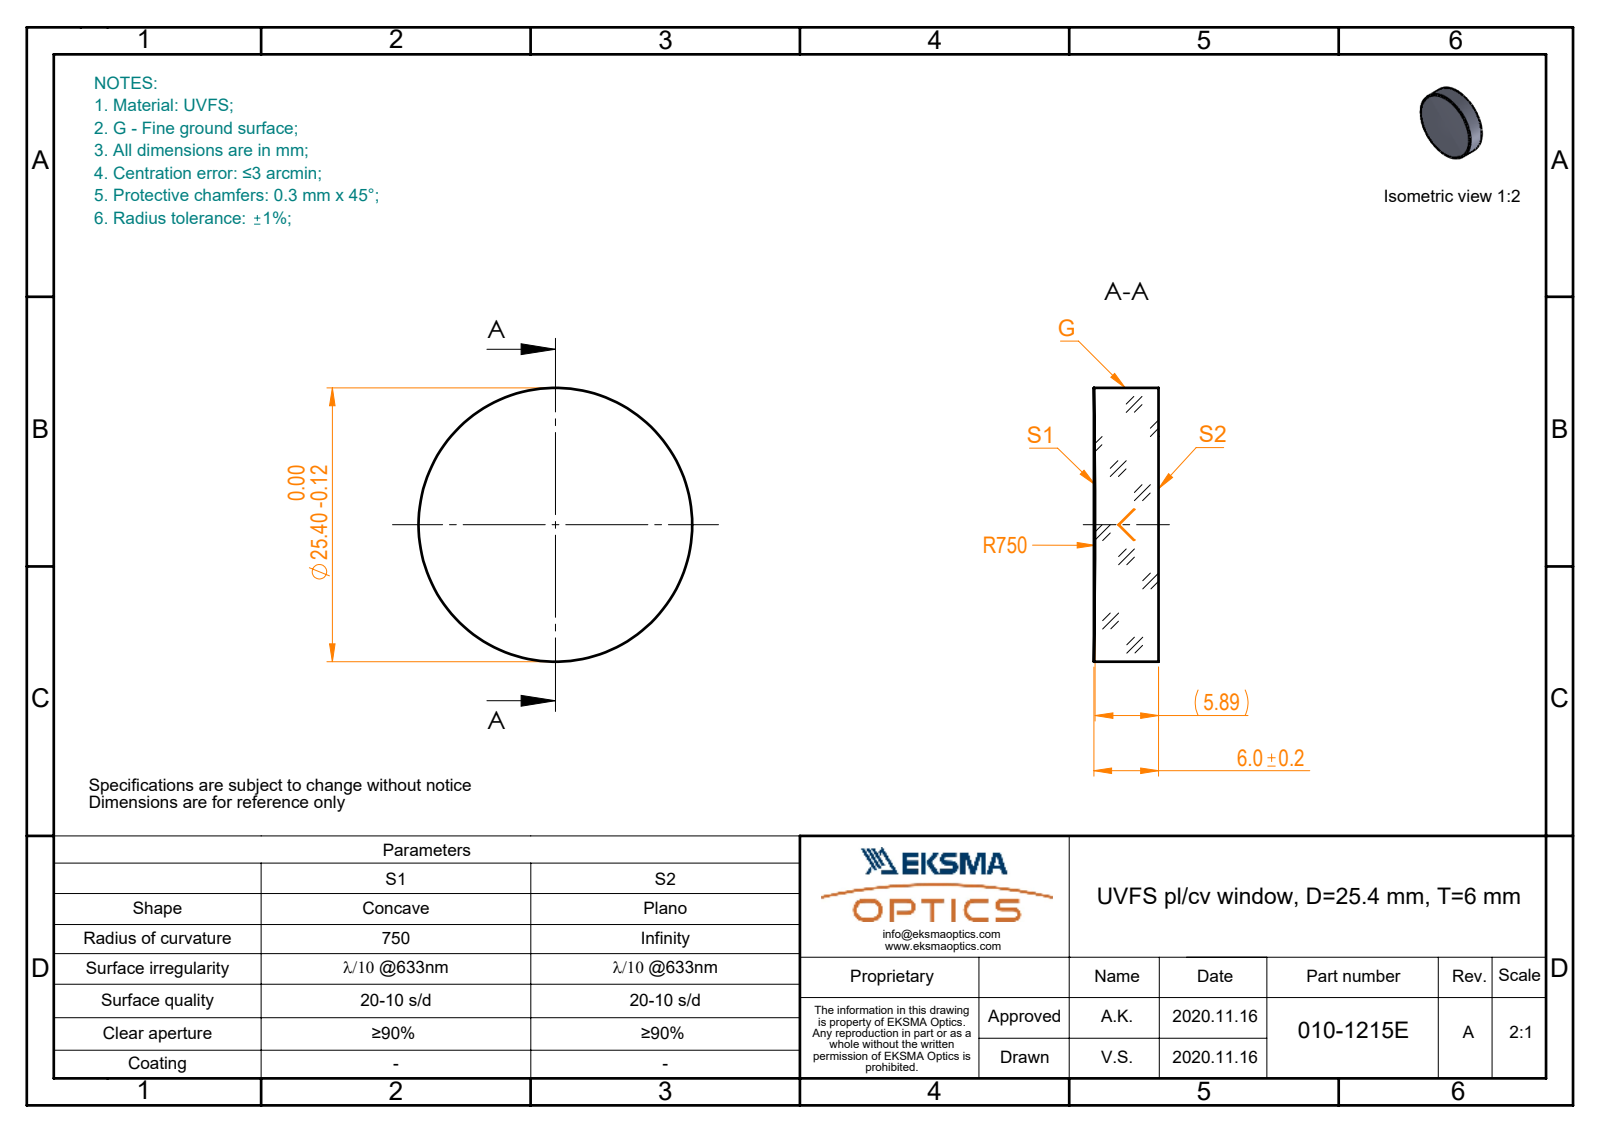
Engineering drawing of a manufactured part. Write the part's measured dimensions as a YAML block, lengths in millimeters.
part_name: "010-1215E_UVFS_PCV_window"
step_written_by: "SolidWorks 2019 (CONFIG_CONTROL_DESIGN)"
units: millimeters
bodies: {solids: 1, faces: 5, planar: 1, cylindrical: 2, other: 2}
overall_size: [25.4, 25.4, 6]
volume: 3013
surface_area: 1492
round_bosses_or_shafts:
  - {diameter: 25.4, count: 1}
